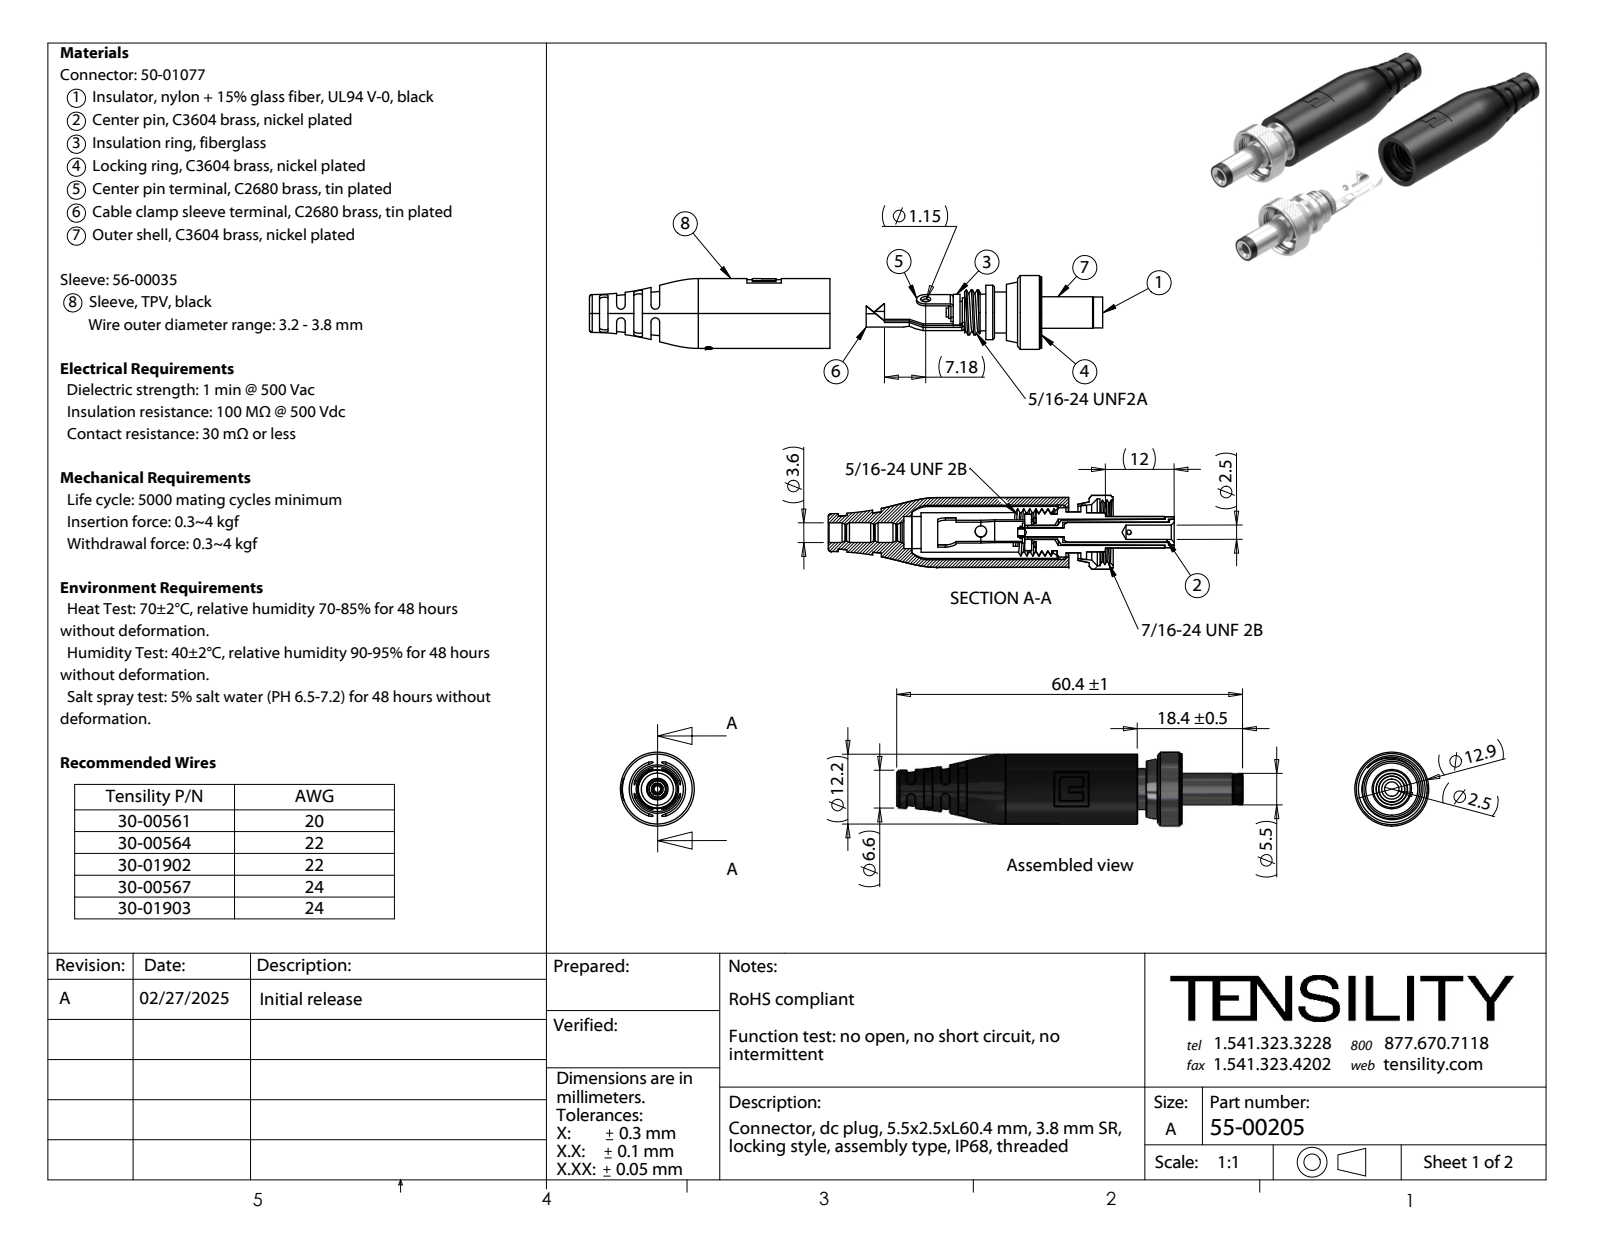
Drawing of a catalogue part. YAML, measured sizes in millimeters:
part_name: "50-01077_Center pin terminal; 50-01077_Floating locking ring_Step; 3.6(3.2-3.8); 50-01077_Cable clamp sleeve terminal (+8 more)"
step_written_by: "SolidWorks 2021 (CONFIG_CONTROL_DESIGN)"
units: millimeters
bodies: {solids: 9, faces: 400, planar: 128, cylindrical: 146, other: 126}
overall_size: [61.03, 12.9, 12.9]
volume: 3501
surface_area: 7091
round_holes:
  - {diameter: 1.15, count: 2}
  - {diameter: 0.8, count: 1}
  - {diameter: 1.6, count: 1}
  - {diameter: 2, count: 1}
  - {diameter: 2.45, count: 1}
  - {diameter: 2.5, count: 1}
  - {diameter: 3.35, count: 1}
  - {diameter: 3.55, count: 1}
  - {diameter: 4.55, count: 1}
  - {diameter: 4.6, count: 1}
  - {diameter: 5.6, count: 1}
  - {diameter: 6.9, count: 1}
round_bosses_or_shafts:
  - {diameter: 12.9, count: 1}
  - {diameter: 12.4, count: 1}
  - {diameter: 12.2, count: 1}
  - {diameter: 7.85, count: 1}
  - {diameter: 7.15, count: 1}
  - {diameter: 6.85, count: 1}
  - {diameter: 6.4, count: 1}
  - {diameter: 5.5, count: 1}
partial_cylinders:
  - {radius: 0.75, count: 8}
  - {radius: 0.2, count: 4}
  - {radius: 1.57, count: 2}
  - {radius: 6.1, count: 2}
  - {radius: 0.1, count: 1}
  - {radius: 0.4, count: 1}
  - {radius: 0.5, count: 1}
  - {radius: 0.6, count: 1}
face_to_face_distances: [29.88, 0.4, 1.5, 4.1, 5.07, 3.7, 1.37, 1.7, 0.33, 3.37]
